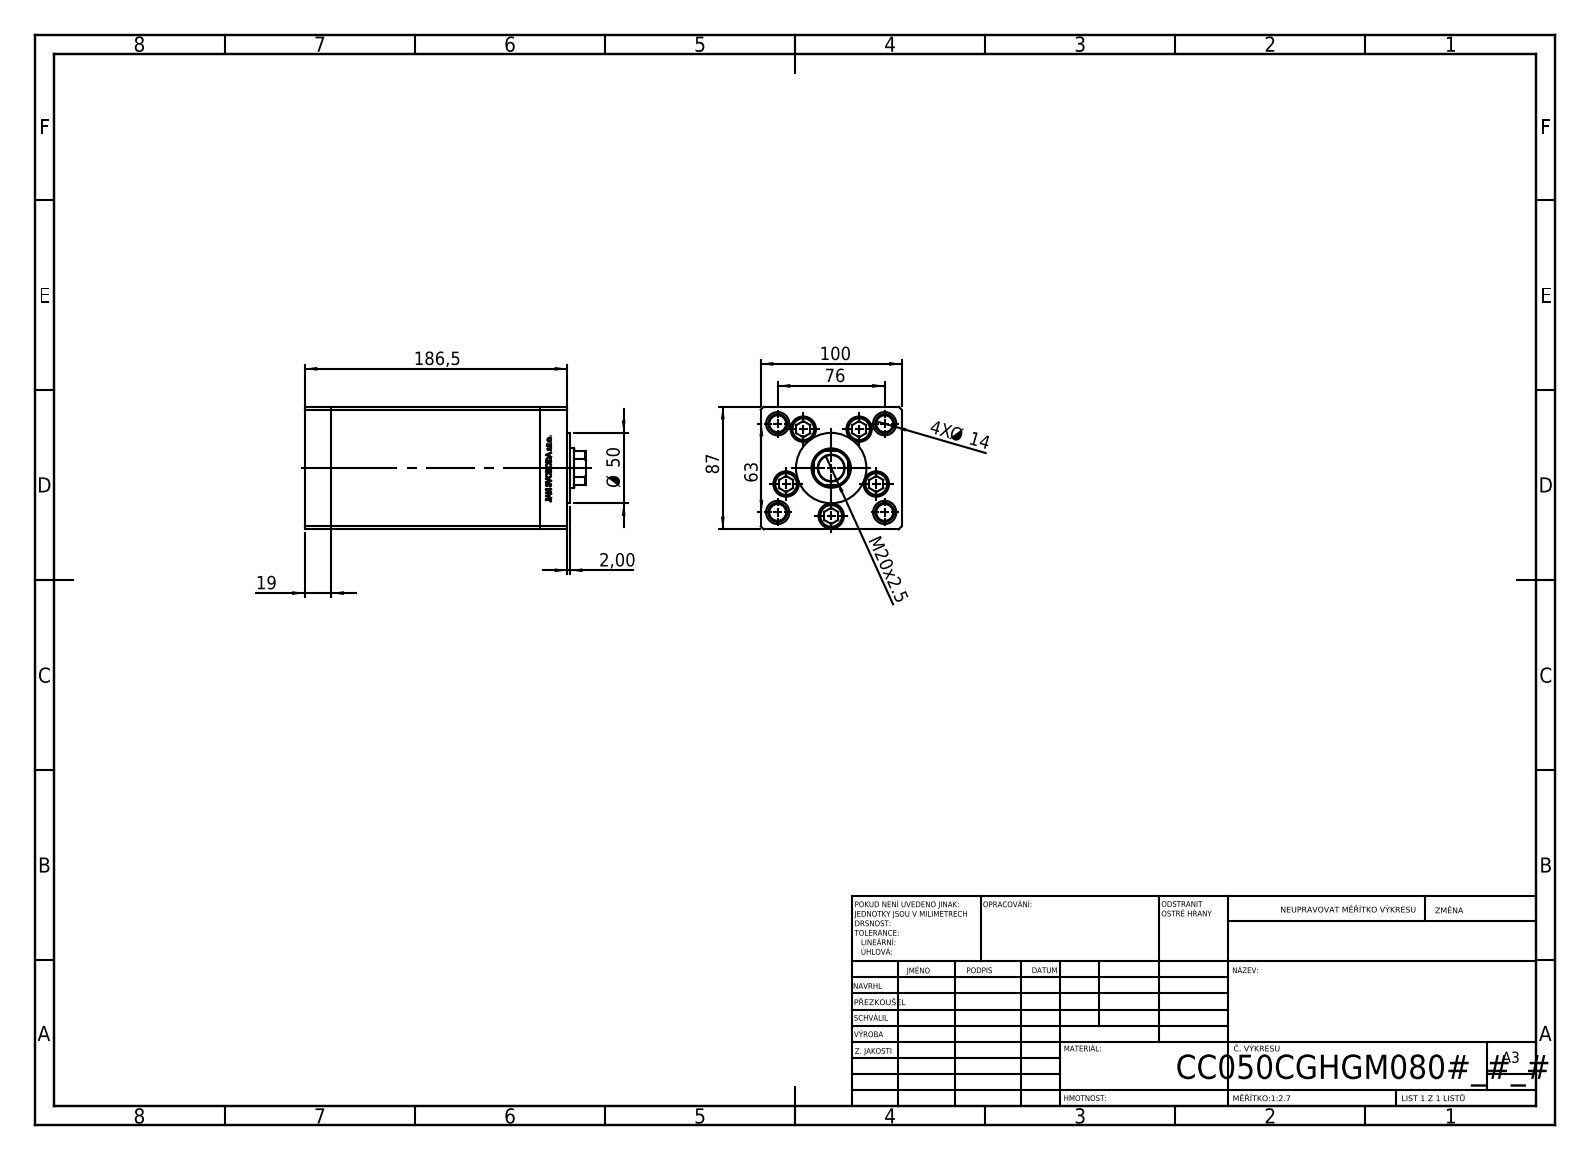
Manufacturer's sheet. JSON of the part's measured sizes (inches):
{"part_name": "ALLEN BOLT; V220C FRONT; V220C BACK_C; V220C_VC_C (+1 more)", "step_written_by": "SolidWorks 2019 (CONFIG_CONTROL_DESIGN)", "units": "inches", "bodies": {"solids": 13, "faces": 1182, "planar": 544, "cylindrical": 176, "other": 462}, "overall_size": [7.854, 3.937, 3.425], "volume_in3": 81.04, "surface_area_in2": 357.8, "round_holes": [[0.531, 9], [0.709, 5], [0.079, 4], [0.472, 4], [0.518, 4], [0.65, 4], [0.669, 1], [0.728, 1], [1.102, 1]], "round_bosses_or_shafts": [[0.315, 5], [0.669, 4], [1.969, 1]], "partial_cylinders_radius": [[0.037, 2], [0.531, 1]], "face_to_face_distances": [3.937, 3.425, 0.748, 5.846, 6.594, 1.348, 7.343, 5.994, 5.246, 0.6], "hole_center_spacings": [1.339, 1.943, 0.732, 0.828, 1.499, 1.546, 1.607, 1.702]}
